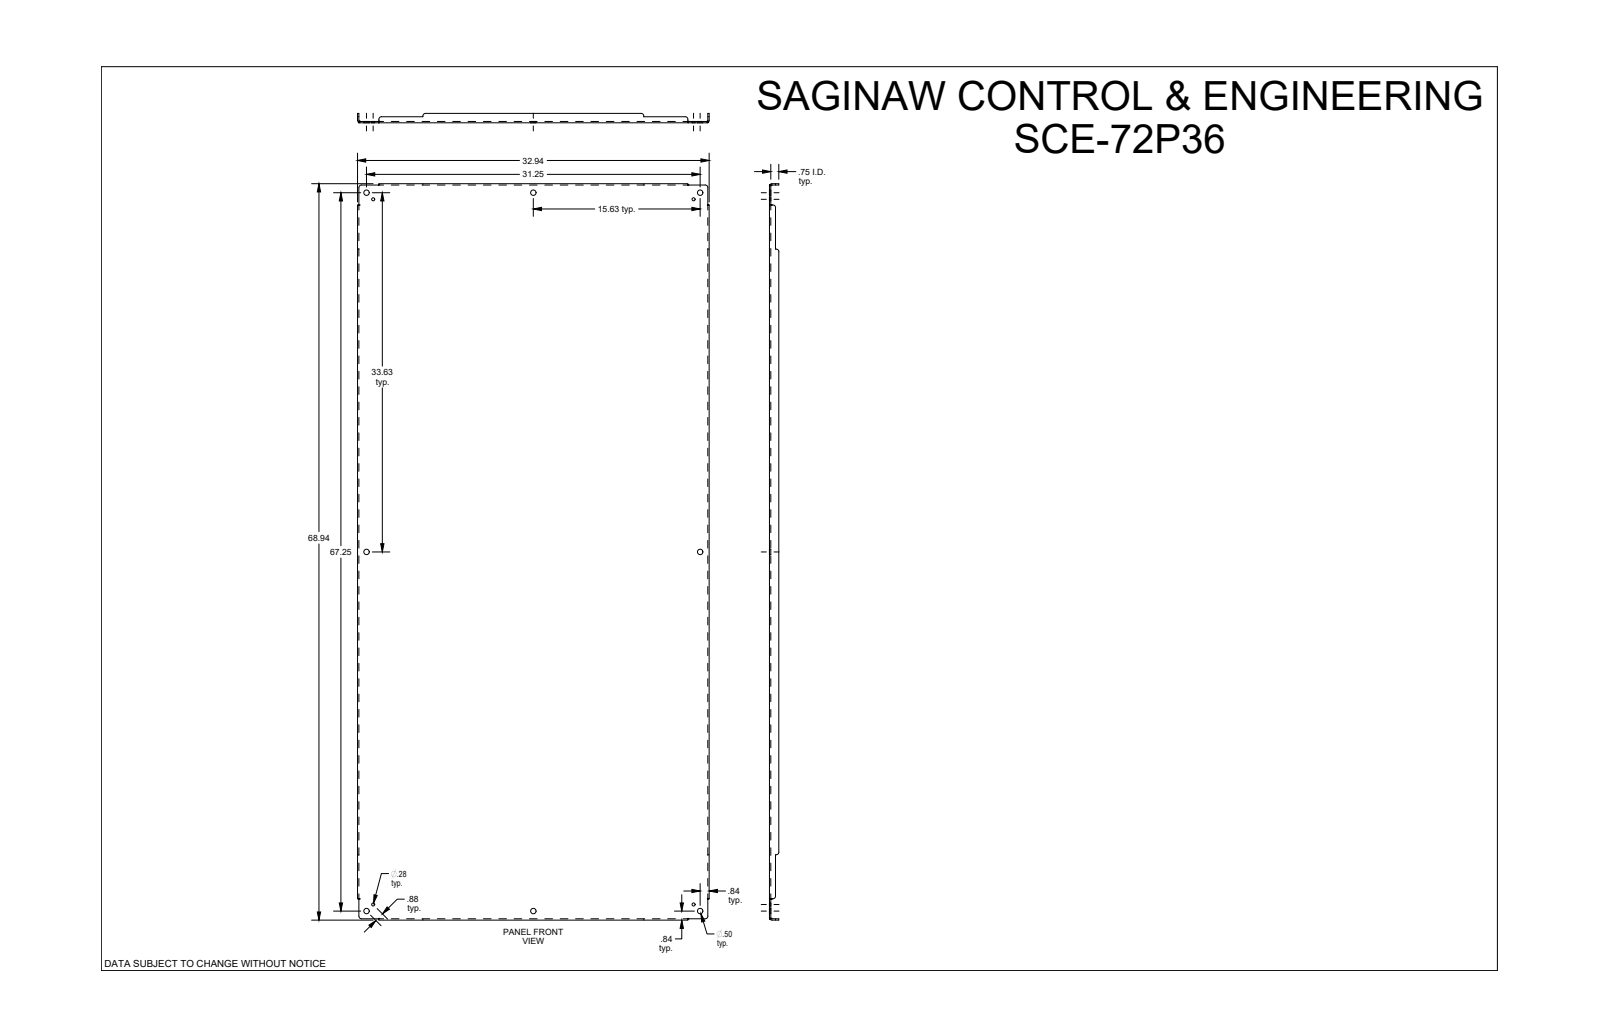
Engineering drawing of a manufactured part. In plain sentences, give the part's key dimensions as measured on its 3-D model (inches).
The part is named "SCE-72P36". Its 3-D file was written by "SolidWorks 2019 (CONFIG_CONTROL_DESIGN)". It is 1 solid with 110 faces: 46 planar, 40 cylindrical and 24 other. Overall it measures 68.938 by 32.938 by 0.875 inches. Its volume is 297.9 cubic inches and its surface area 4 794 square inches. Round holes: 8 of diameter 0.5, 4 of diameter 0.281. Partial cylindrical surfaces (rounded edges, fillets, slot ends): 12 of radius 0.25, 4 of radius 0.112, 4 of radius 0.237. The main face-to-face distances are 0.125, 0.125, 32.813, 32.687, 32.938, 68.813, 0.75, 0.875, 68.687, 68.938. The hole center spacings are 0.875, 15.019, 15.625, 30.638, 33.012, 33.625, 37.078, 45.03.
